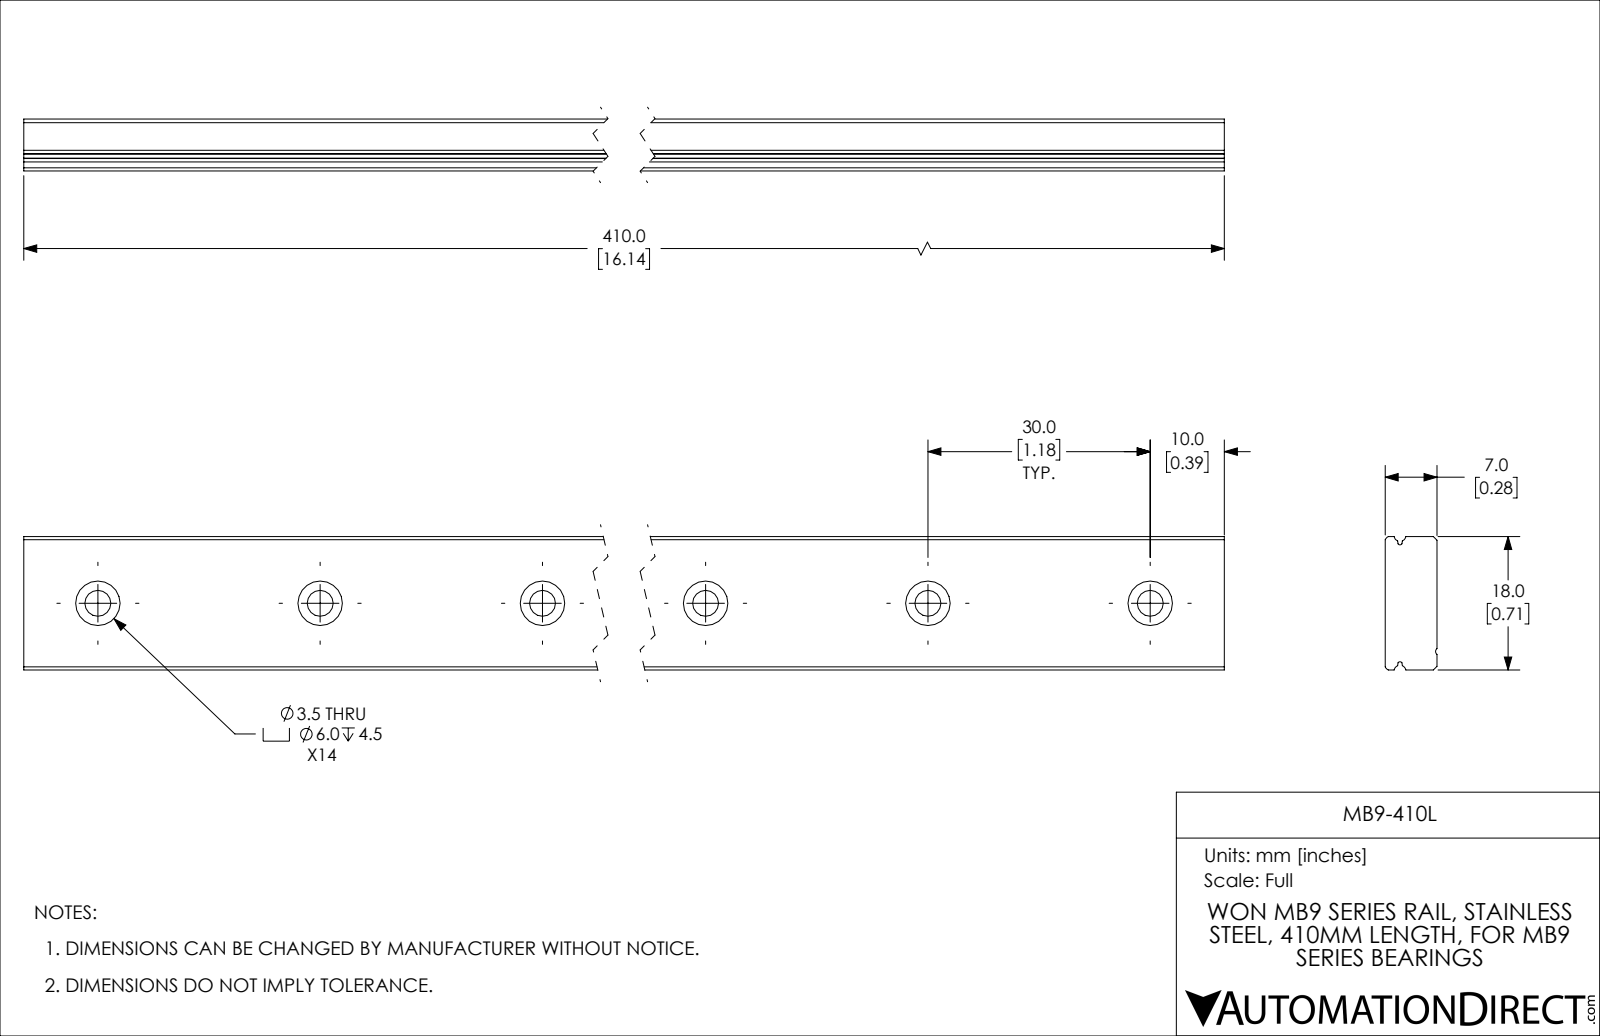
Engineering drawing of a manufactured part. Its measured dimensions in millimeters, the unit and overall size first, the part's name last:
Units: millimetres
Overall size (bounding box): 410 × 18 × 7
Round holes (diameter × count): ⌀3.5 ×14, ⌀6 ×14
Partial cylindrical surfaces — rounded edges, fillets, slot ends (radius × count): R0.32 ×2, R0.8 ×2, R0.95 ×2, R0.5 ×1
Main face-to-face distances: 7, 18, 1.63, 2.5, 4.5, 410
Hole centre spacings: 30, 60, 90, 120, 150, 180, 210, 240
Volume: 48 495 mm³ · Surface area: 22 817 mm²
Bodies: 1 solid, 95 faces (29 planar, 66 cylindrical, 0 other)
Part name (STEP PRODUCT): MB9-410L
STEP written by: SolidWorks 2019 (CONFIG_CONTROL_DESIGN)
